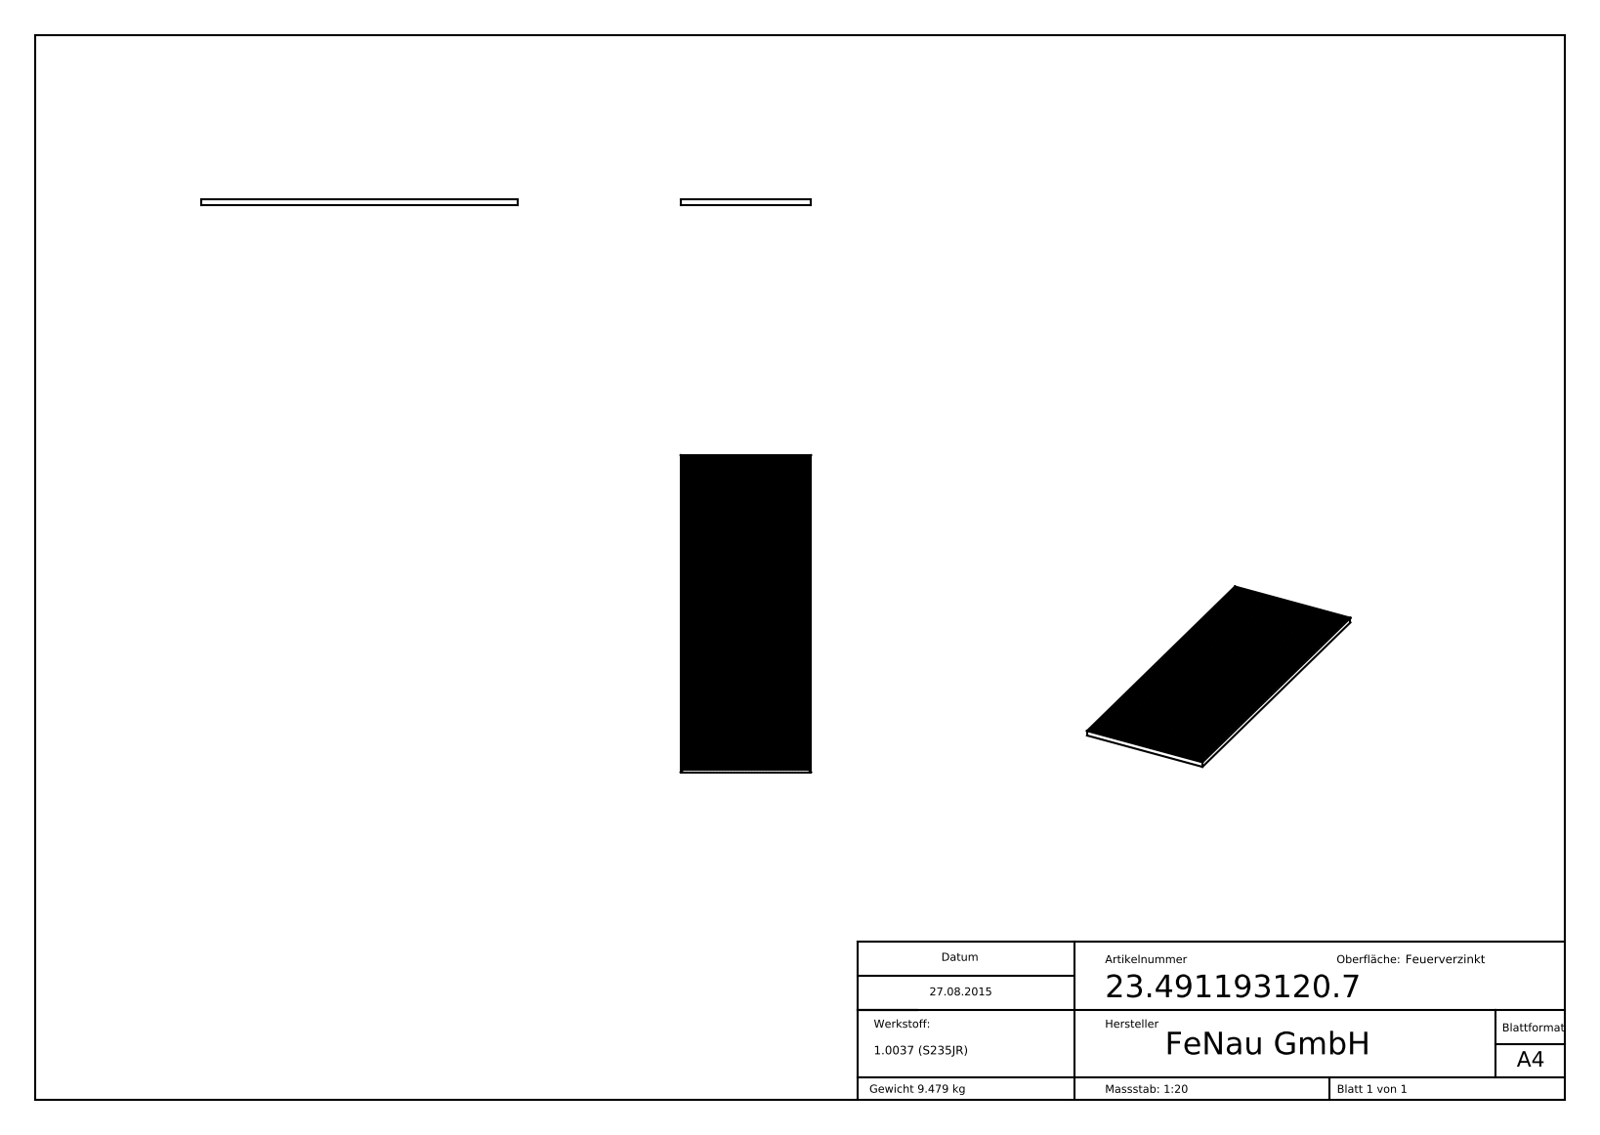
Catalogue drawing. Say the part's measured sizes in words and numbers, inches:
The part is named "23-491193120-7". Its 3-D file was written by "SolidWorks 2015 (CONFIG_CONTROL_DESIGN)". It is 1 solid with 5698 faces: 5698 planar, 0 cylindrical and 0 other. Overall it measures 46.85 by 19.291 by 0.787 inches. Its volume is 74.14 cubic inches and its surface area 3 137 square inches. The main face-to-face distances are 0.433, 0.866, 1.24, 1.299, 2.48, 1.732, 3.72, 2.165, 6.201, 4.961.
